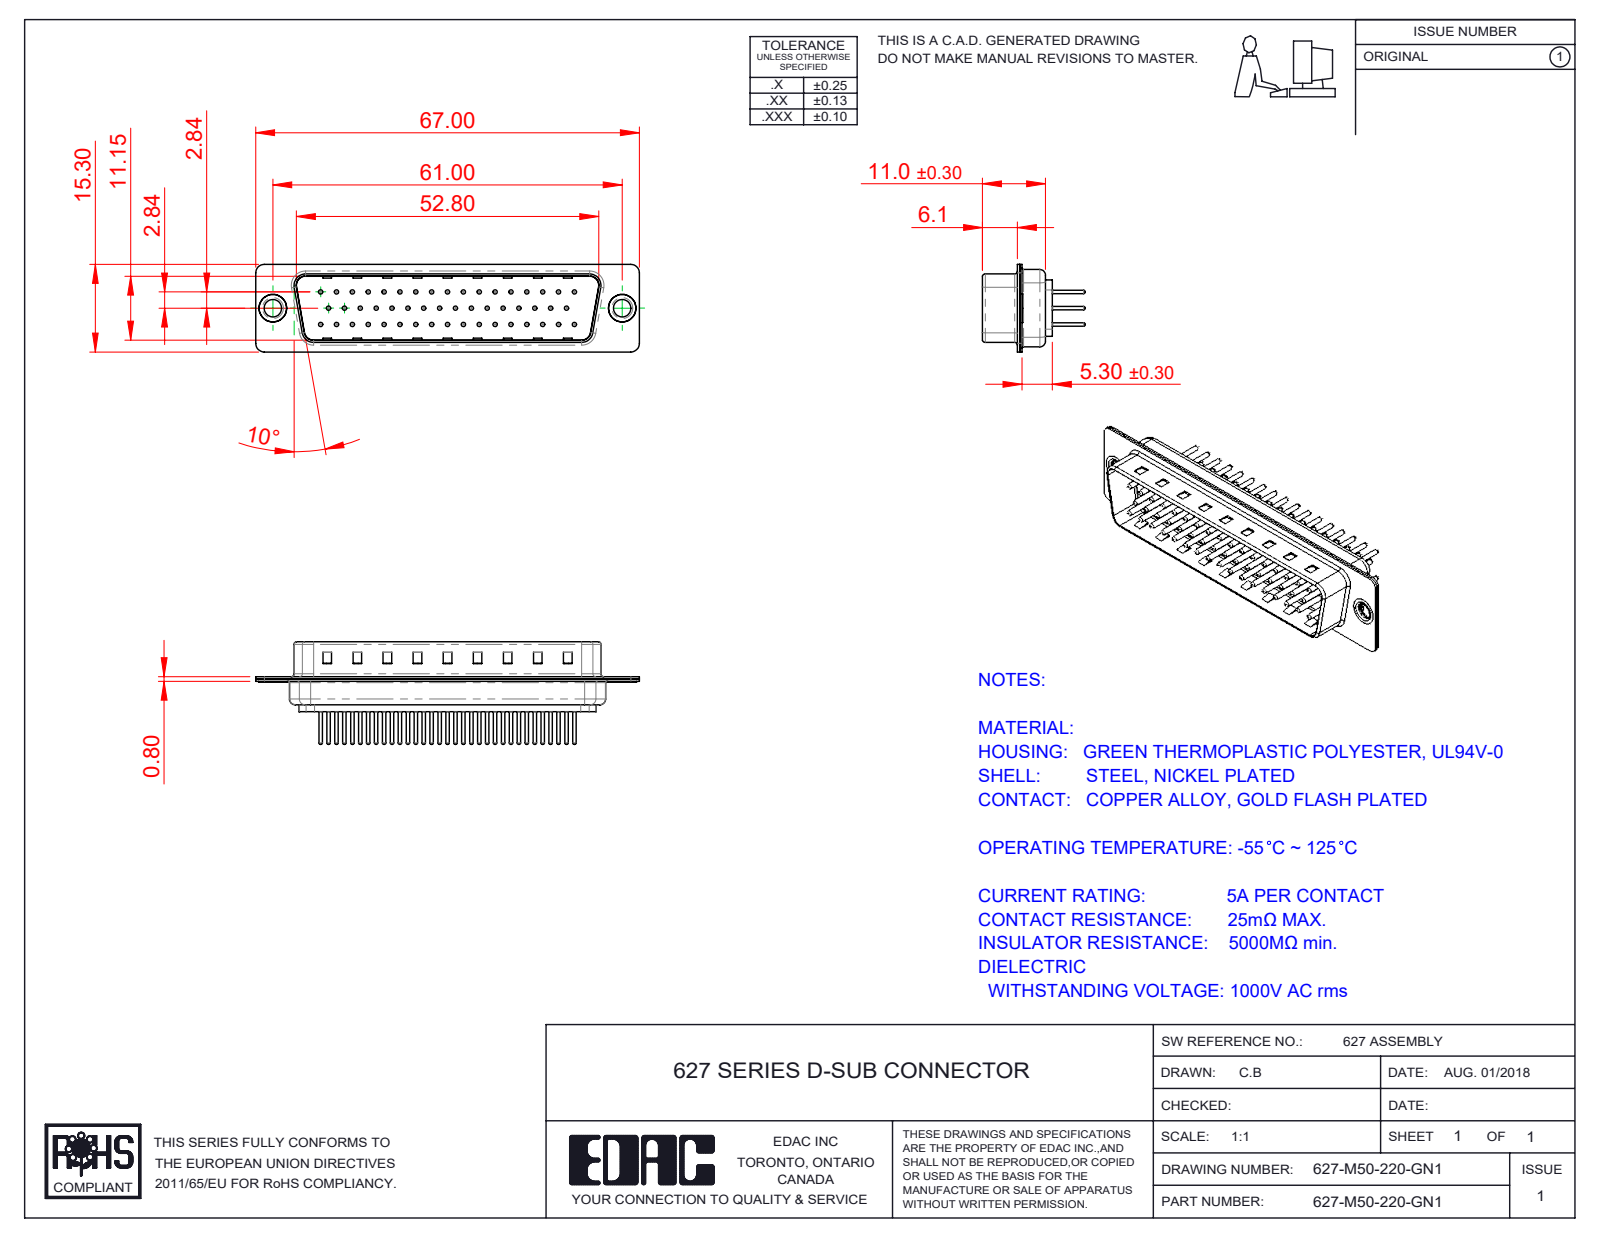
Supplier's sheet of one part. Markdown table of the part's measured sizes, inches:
| quantity | value |
| --- | --- |
| part name | 627-M50-220-GN1; 627M Contact Row 3_20; 627M Shell Front_50 Contacts; 627M Thru Hole Rivet (+4 more) |
| STEP written by | SolidWorks 2020 (CONFIG_CONTROL_DESIGN) |
| units | inches |
| bodies | 55 solids, 2236 faces (553 planar, 825 cylindrical, 858 other) |
| overall size | 2.638 × 0.705 × 0.602 |
| volume | 0.271 in³ |
| surface area | 16.36 in² |
| round holes (diameter × count) | 0.03 × 50, 0.063 × 50, 0.079 × 50, 0.12 × 2, 0.157 × 2, 0.189 × 2 |
| round bosses / shafts (diameter × count) | 0.059 × 50, 0.024 × 50, 0.197 × 2, 0.193 × 2, 0.14 × 2 |
| partial cylindrical surfaces (radius × count) | 0.059 × 16, 0.079 × 12, 0.02 × 8, 0.063 × 8, 0.01 × 4, 0.024 × 4, 0.026 × 4, 0.035 × 4 |
| main face-to-face distances | 0.016, 0.455, 0.224, 0.24, 0.031, 0.03, 0.485, 0.485, 0.516, 0.209 |
| hole center spacings | 0.124, 0.109, 0.218, 0.327, 0.436, 0.545, 0.654, 0.198 |
